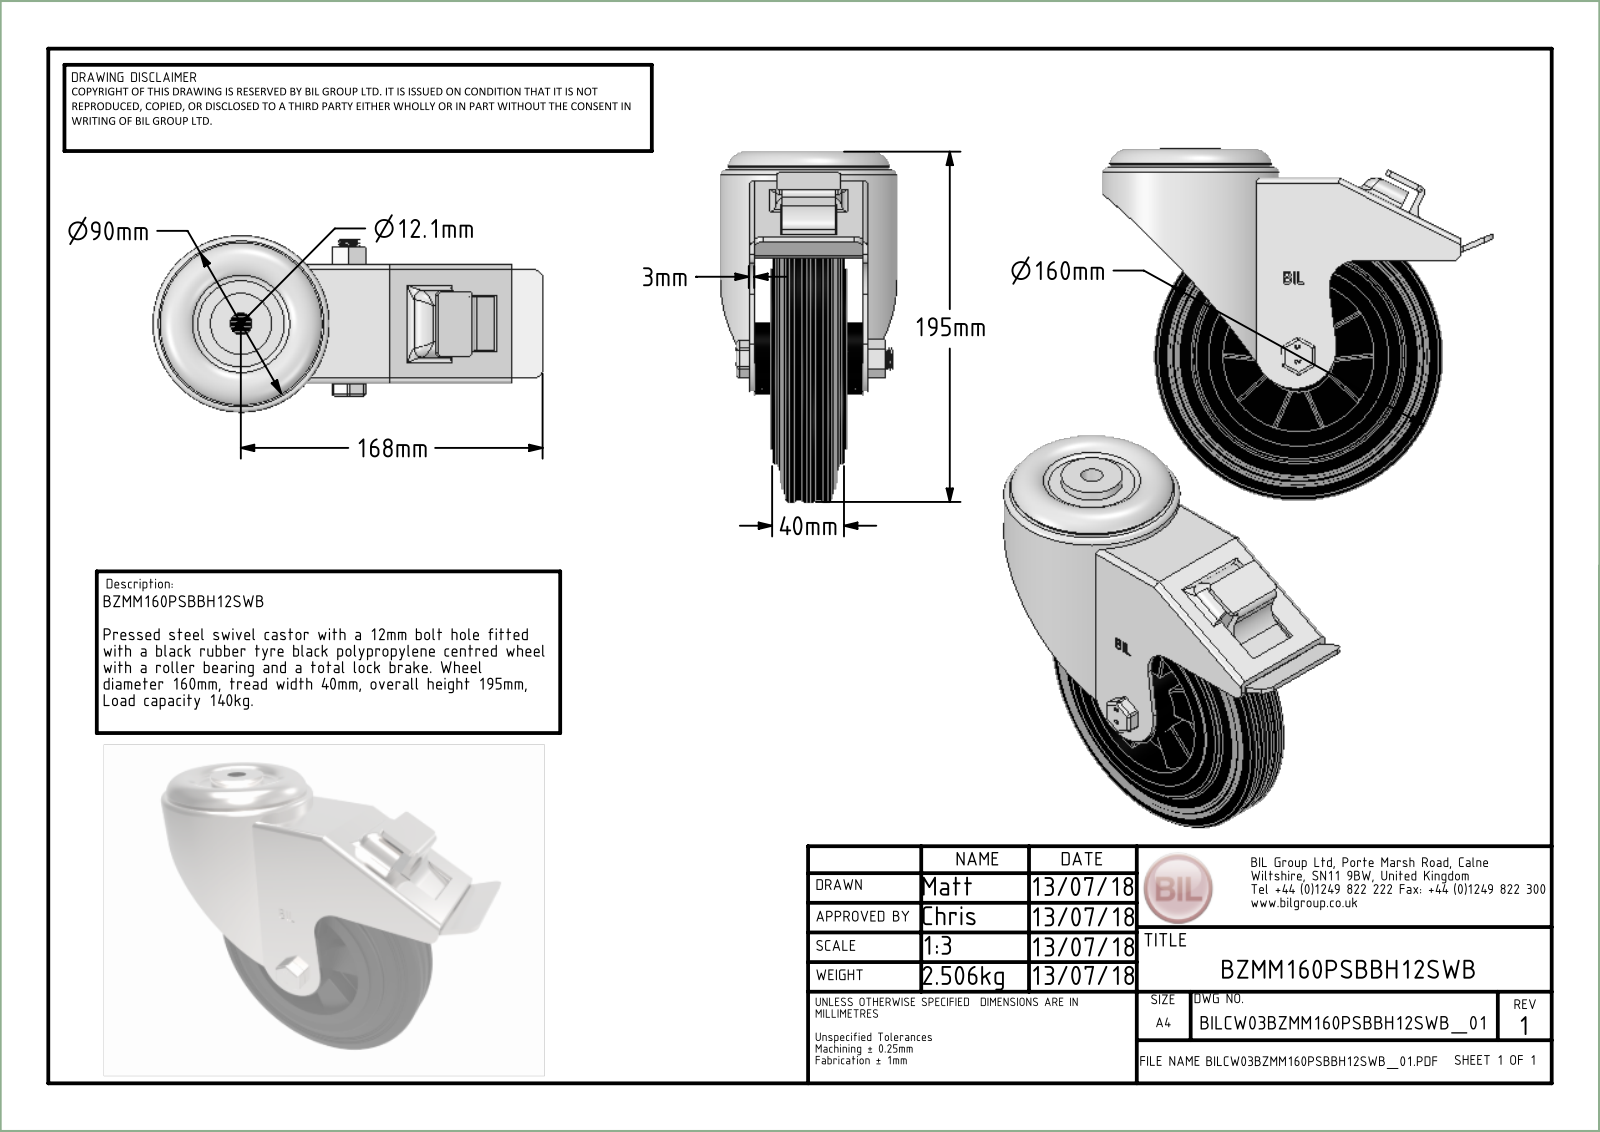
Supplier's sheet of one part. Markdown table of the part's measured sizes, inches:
| quantity | value |
| --- | --- |
| part name | BZMM160PSBBH12SWB v3; BZMM150ASBH12SWB v1; ZINC PLATED, PRESSED STEEL TOP PLATE; ZINC PLATED, PRESSED STEEL FORKS (+8 more) |
| STEP written by | Autodesk Translation Framework v13.20.0.188 (AP242_MANAGED_MODEL_BASED_3D_ENGINEERING_MIM_LF) |
| units | inches |
| bodies | 23 solids, 935 faces (364 planar, 217 cylindrical, 354 other) |
| overall size | 8.78 × 7.677 × 4.331 |
| volume | 47.58 in³ |
| surface area | 432.8 in² |
| round holes (diameter × count) | 0.315 × 2, 1.339 × 2, 0.472 × 1, 0.476 × 1, 0.48 × 1, 0.492 × 1, 0.551 × 1, 0.787 × 1, 1.319 × 1, 1.378 × 1, 2.067 × 1, 2.579 × 1 |
| round bosses / shafts (diameter × count) | 0.295 × 8, 1.575 × 2, 6.236 × 1, 4.331 × 1, 3.976 × 1, 3.031 × 1, 1.374 × 1, 0.984 × 1 |
| partial cylindrical surfaces (radius × count) | 0.02 × 24, 0.039 × 18, 0.059 × 12, 0.118 × 8, 0.079 × 3, 0.098 × 3, 0.157 × 2, 0.236 × 2 |
| main face-to-face distances | 0.118, 2.48, 0.187, 0.059, 0.098, 0.305, 0.069, 2.362, 0.128, 0.453 |
| hole center spacings | 2.717 |
